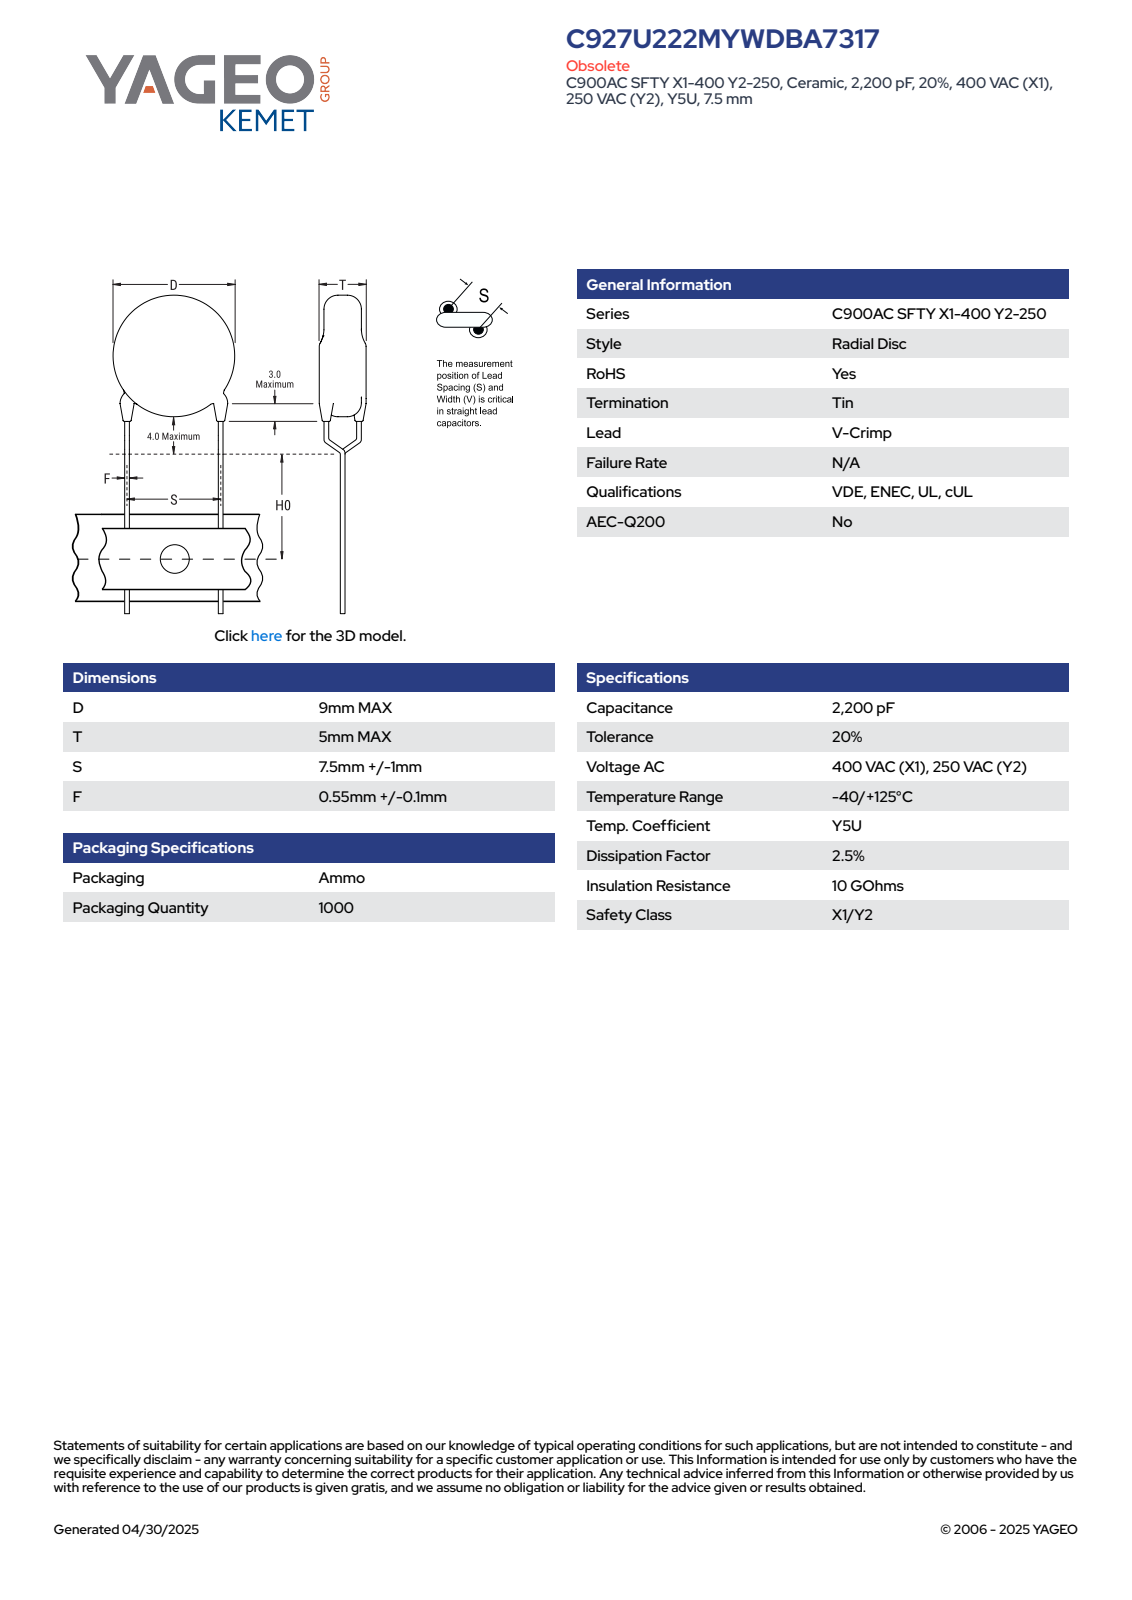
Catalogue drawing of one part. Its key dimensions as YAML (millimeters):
part_name: "CCD_VCC900_D9T5S7.5LL20F0.65"
step_written_by: "SolidWorks 2014 (AUTOMOTIVE_DESIGN)"
units: millimeters
bodies: {solids: 5, faces: 93, planar: 65, cylindrical: 16, other: 12}
overall_size: [32.8, 9, 5]
volume: 325
surface_area: 359
round_bosses_or_shafts:
  - {diameter: 0.65, count: 6}
  - {diameter: 9, count: 1}
face_to_face_distances: [5, 22.9, 1.17, 28.88, 5.98, 27.71, 4.81, 0.32, 4.77, 3.47]
